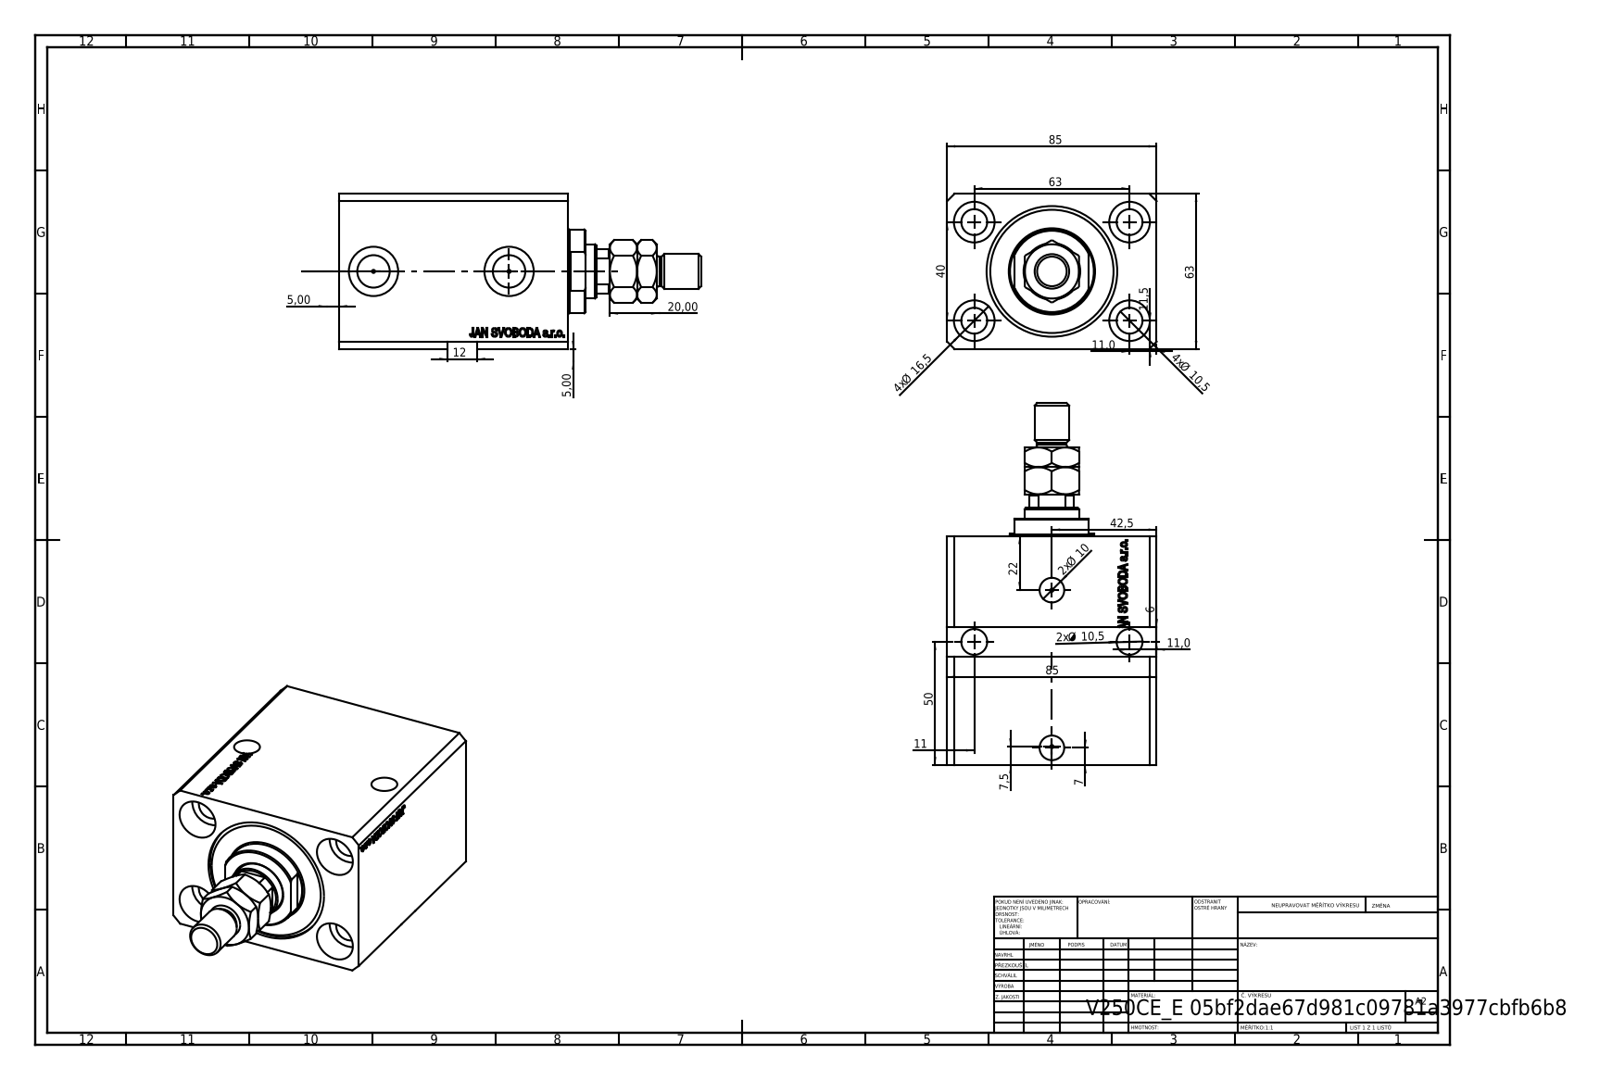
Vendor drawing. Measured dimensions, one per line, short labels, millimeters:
name: V250CE_C_VCP; V250CE_E_Body; MTA; V250CE_VC_E
written by: SolidWorks 2019 (CONFIG_CONTROL_DESIGN)
unit: mm
bodies: 4 solids, 966 faces (474 planar, 88 cylindrical, 404 other)
size: 146.9 × 85 × 63
volume: 437 690 mm³; area: 92 452 mm²
holes: 6× ⌀10.5, 4× ⌀1.25, 4× ⌀16.5, 2× ⌀10, 2× ⌀13.16, 2× ⌀20, 1× ⌀12.5, 1× ⌀22, 1× ⌀40, 1× ⌀53
bosses: 1× ⌀34, 1× ⌀14, 1× ⌀12
rounds: 1× R10.5
face distances: 63, 85, 93, 65.9, 27.1, 11.4, 54.5, 81.6, 44, 11
hole spacings: 37.31, 63, 37.86, 40, 52.88, 53.3, 74.63, 0.53
